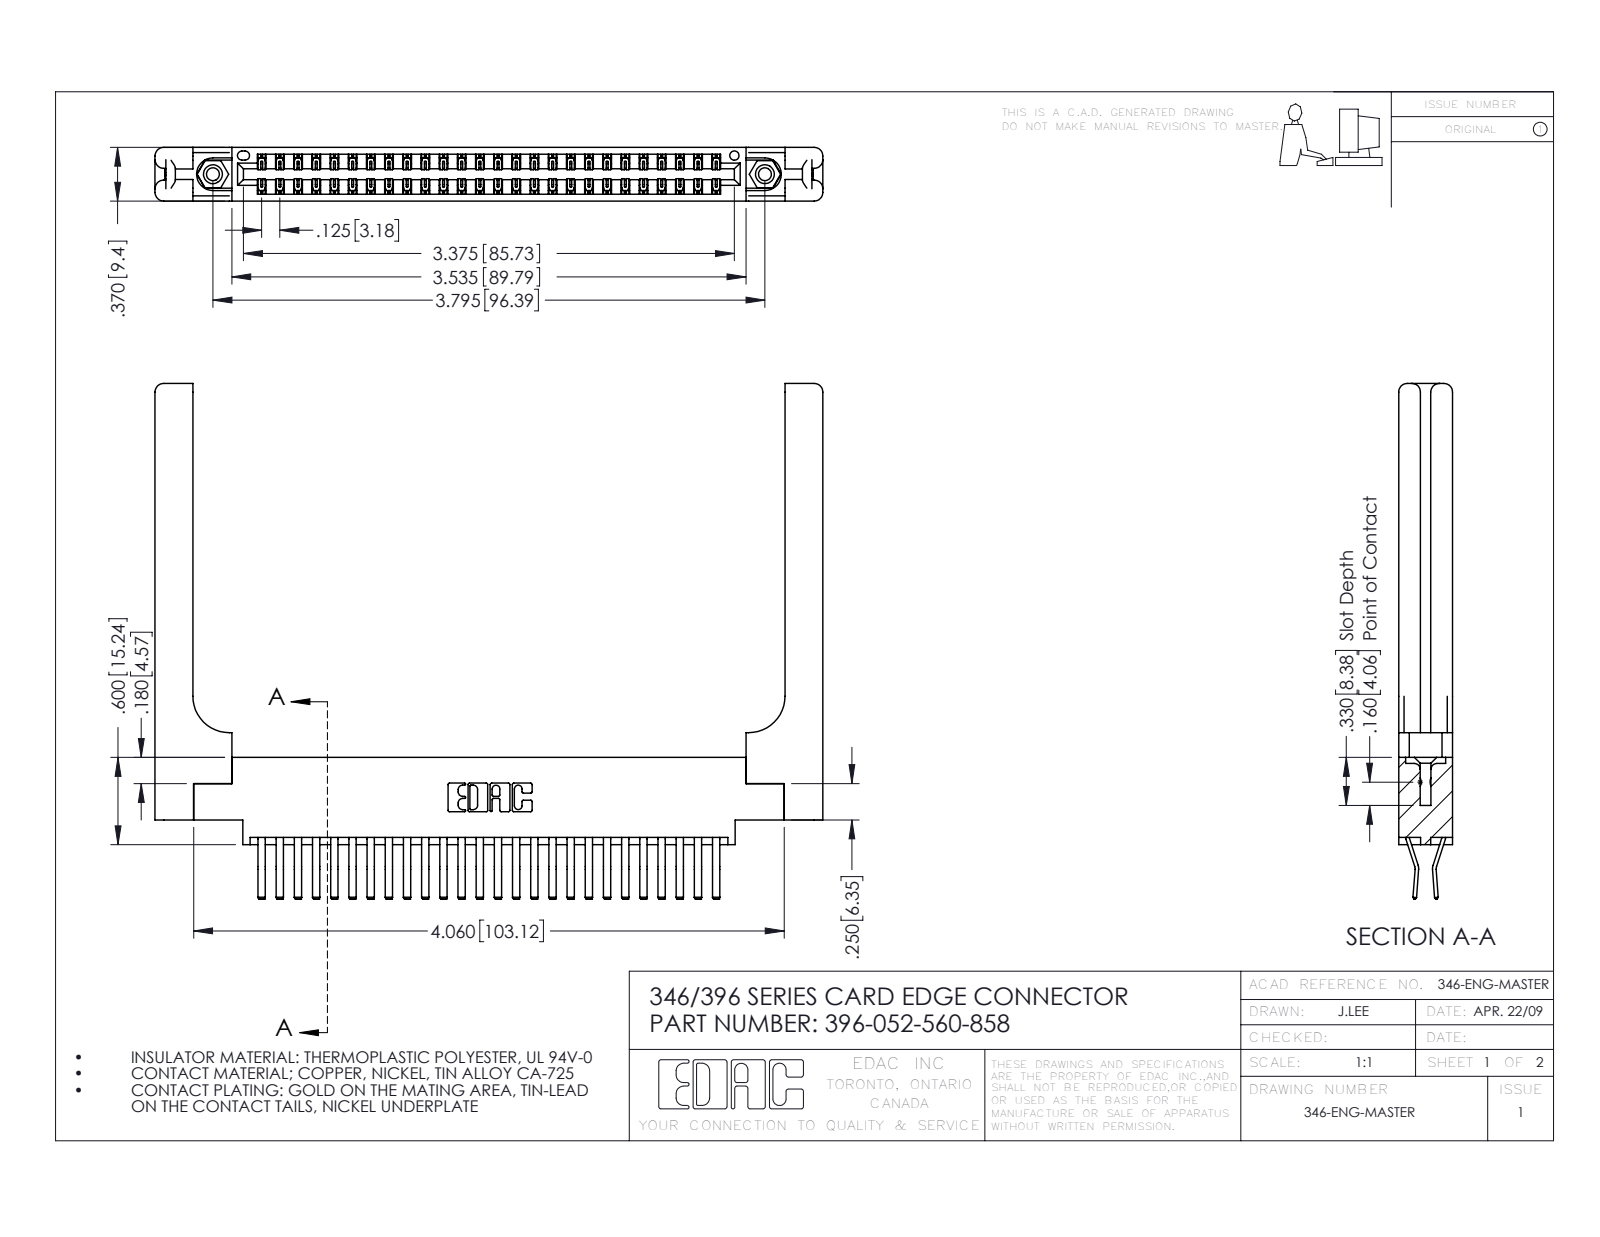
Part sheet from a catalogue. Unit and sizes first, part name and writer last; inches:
Units: inches
Overall size (bounding box): 4.591 × 3.545 × 0.37
Round holes (diameter × count): ⌀0.089 ×2, ⌀0.125 ×2, ⌀0.156 ×2, ⌀0.064 ×1
Round bosses / shafts (diameter × count): ⌀0.155 ×2
Partial cylindrical surfaces — rounded edges, fillets, slot ends (radius × count): R0.006 ×78, R0.01 ×22, R0.06 ×16, R0.007 ×6, R0.031 ×6, R0.026 ×3, R0.01 ×2, R0.014 ×2
Main face-to-face distances: 0.37, 0.072, 0.048, 0.322, 0.148, 0.15, 0.025, 0.25, 0.298, 0.275
Hole centre spacings: 0.246, 3.587, 3.795
Volume: 1.155 in³ · Surface area: 33.36 in²
Bodies: 57 solids, 3190 faces (2048 planar, 1082 cylindrical, 60 other)
Part name (STEP PRODUCT): 345-292-001_560 Tail; 345-250-001_345-250-001-102; 346 Part_0.170 Offset - 0.156 Dia-TH; 346-220-058_345-220-058 (+1 more)
STEP written by: SolidWorks 2016 (CONFIG_CONTROL_DESIGN)
